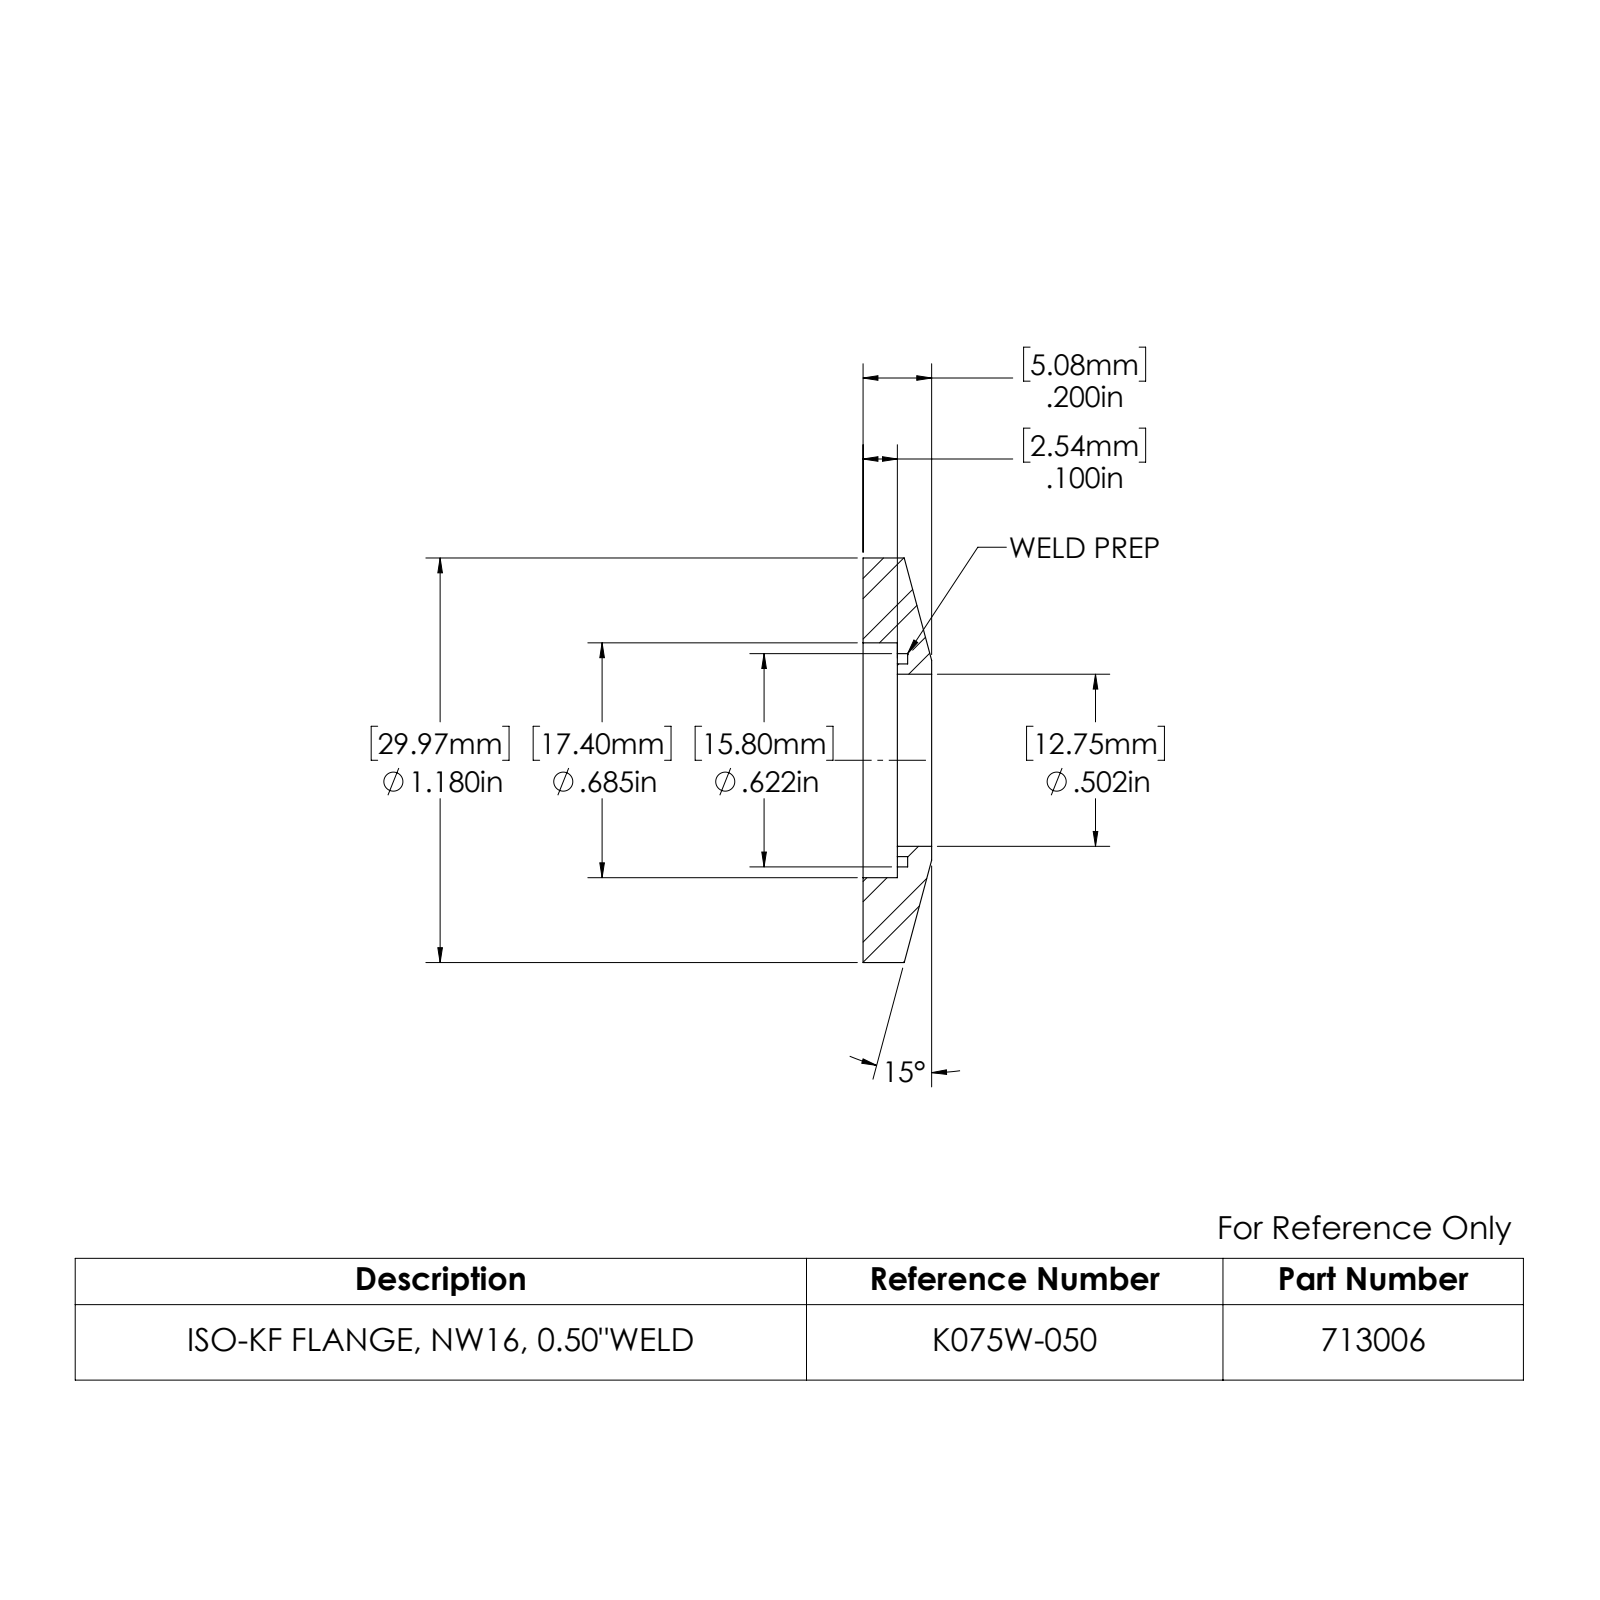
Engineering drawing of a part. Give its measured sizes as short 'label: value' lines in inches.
name: 713006
written by: SolidWorks 2022 (AUTOMOTIVE_DESIGN)
unit: in
bodies: 1 solid, 17 faces (5 planar, 10 cylindrical, 2 other)
size: 1.18 × 1.18 × 0.2
volume: 0.124 in³; area: 2.75 in²
holes: 1× ⌀0.502, 1× ⌀0.622, 1× ⌀0.685
bosses: 1× ⌀1.18, 1× ⌀0.562
face distances: 0.1, 0.2, 0.07, 0.03, 0.13
